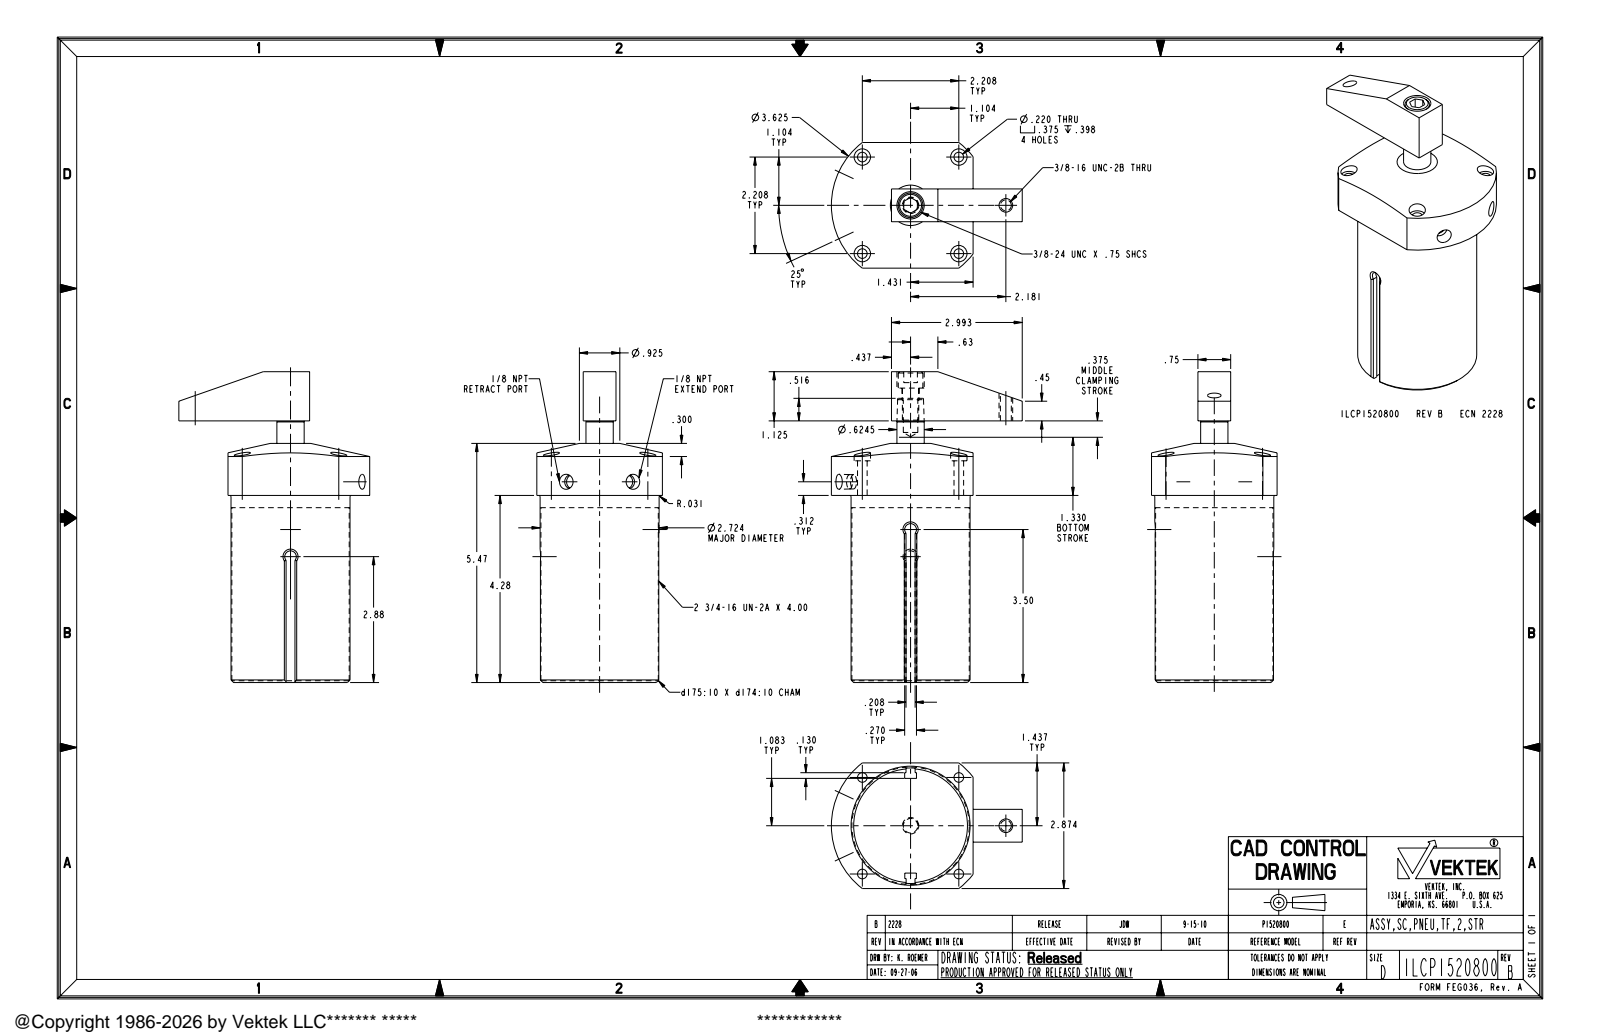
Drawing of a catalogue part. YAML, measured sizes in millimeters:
part_name: "ILCP1520800; ILC91501503; ILCP1520800_ASM"
step_written_by: "PRO/ENGINEER BY PARAMETRIC TECHNOLOGY CORPORATION, 2007460 (AUTOMOTIVE_DESIGN_CC2)"
units: millimeters
bodies: {solids: 2, faces: 123, planar: 52, cylindrical: 47, other: 24}
overall_size: [180.6, 111, 73]
volume: 577500
surface_area: 79610
round_holes:
  - {diameter: 5.6, count: 4}
  - {diameter: 9.5, count: 4}
  - {diameter: 8.3, count: 2}
  - {diameter: 7.9, count: 1}
  - {diameter: 8.4, count: 1}
  - {diameter: 9.9, count: 1}
  - {diameter: 15.9, count: 1}
round_bosses_or_shafts:
  - {diameter: 69.2, count: 1}
  - {diameter: 68.2, count: 1}
  - {diameter: 15.8, count: 1}
  - {diameter: 14.3, count: 1}
  - {diameter: 9.5, count: 1}
  - {diameter: 6.4, count: 1}
partial_cylinders:
  - {radius: 3.4, count: 1}
  - {radius: 3.4, count: 1}
  - {radius: 46, count: 1}
face_to_face_distances: [27, 46, 19.1, 108.7, 73, 43.3, 152, 9, 64, 18]
hole_center_spacings: [39.7, 56.1, 39.2, 79.3, 88, 55.4]
